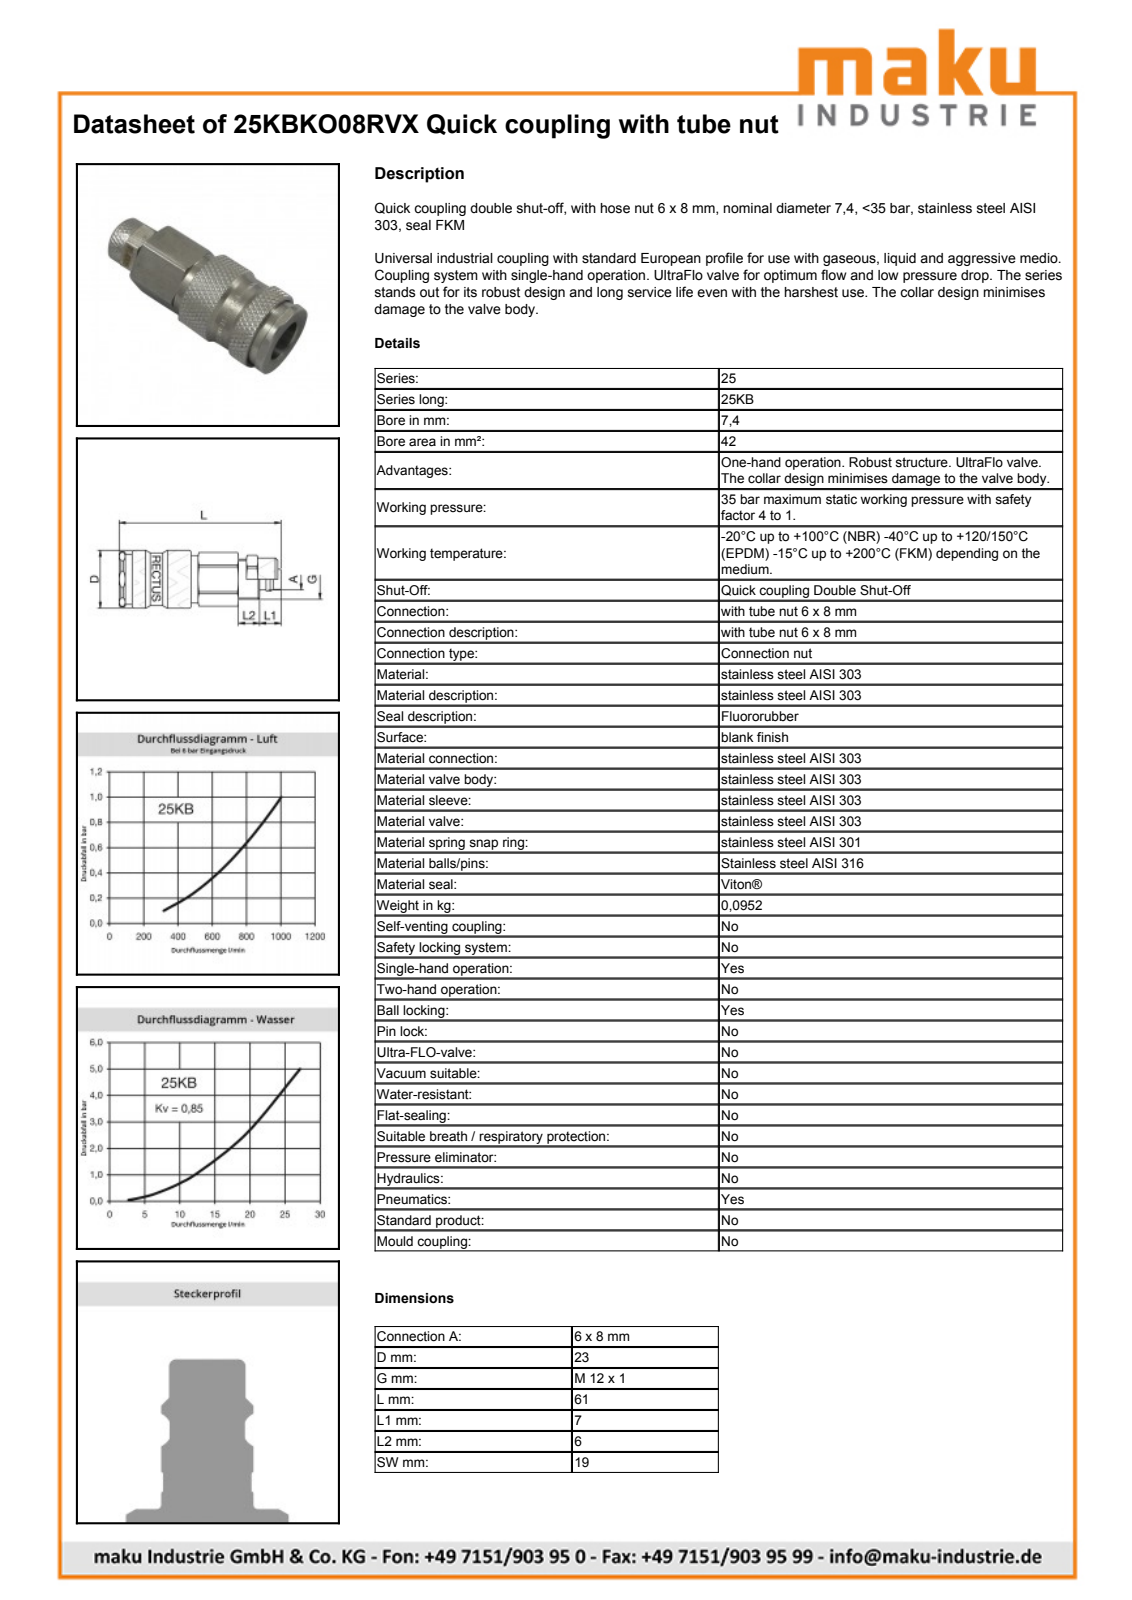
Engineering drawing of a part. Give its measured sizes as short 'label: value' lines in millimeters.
name: D106005
written by: Autodesk Inventor 2011 (AUTOMOTIVE_DESIGN)
unit: mm
bodies: 2 solids, 653 faces (222 planar, 97 cylindrical, 334 other)
size: 60.5 × 23.15 × 23.15
volume: 17 004 mm³; area: 8 606 mm²
holes: 1× ⌀11, 1× ⌀12.1, 1× ⌀12.5, 1× ⌀15.1, 1× ⌀15.6, 1× ⌀17.25, 1× ⌀19.35, 1× ⌀20.05
bosses: 1× ⌀23.15, 1× ⌀21, 1× ⌀20, 1× ⌀18.95, 1× ⌀16, 1× ⌀15.3, 1× ⌀15, 1× ⌀14.91
rounds: 1× R7.75, 1× R10.4, 1× R10.7, 1× R11
face distances: 19, 47.25, 14, 24.5, 22.75, 53.4, 28.9, 6.15, 28.7, 4.2
